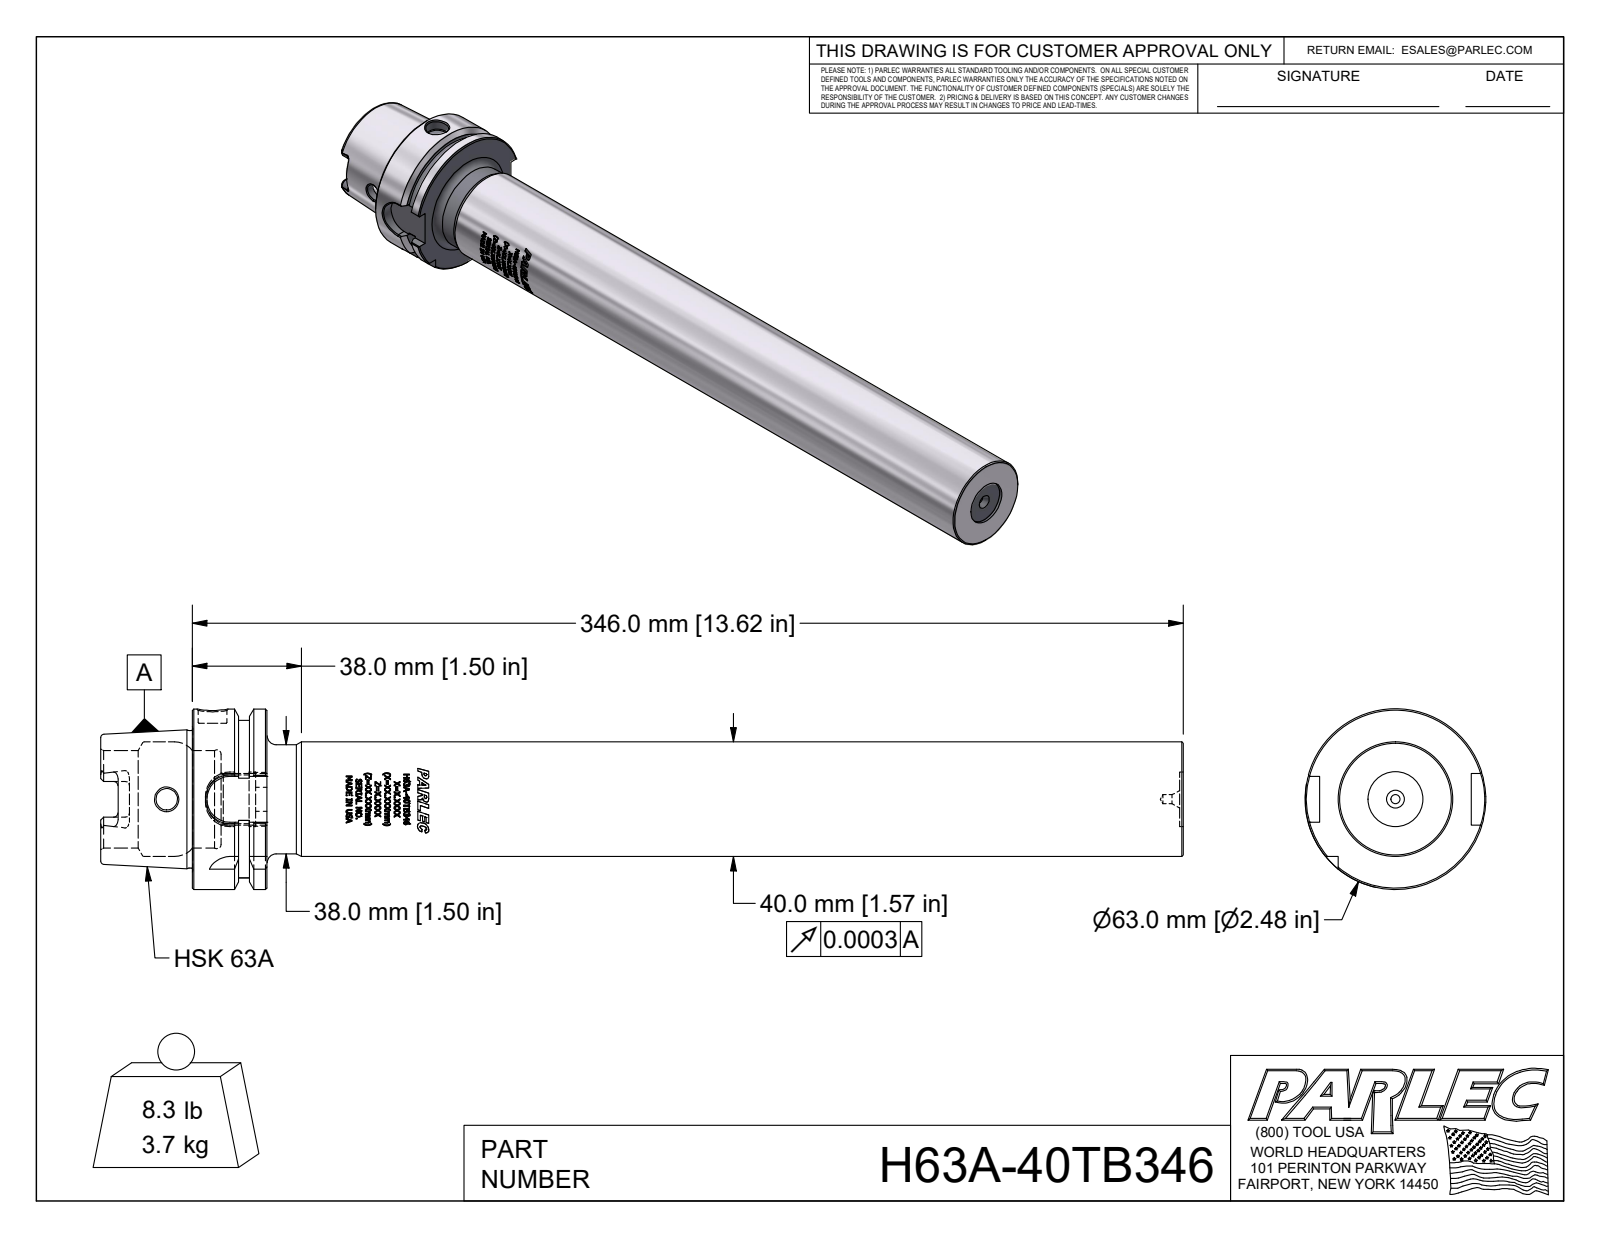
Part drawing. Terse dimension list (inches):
name: H63A-40TB346
written by: Autodesk Inventor 2022 (AUTOMOTIVE_DESIGN)
unit: in
bodies: 1 solid, 1193 faces (501 planar, 134 cylindrical, 558 other)
size: 14.882 × 2.48 × 2.48
volume: 29.4 in³; area: 97.37 in²
holes: 1× ⌀0.125, 1× ⌀0.295, 1× ⌀0.331, 1× ⌀0.394, 1× ⌀0.666, 1× ⌀0.749, 1× ⌀0.75, 1× ⌀1.339
bosses: 1× ⌀2.48, 1× ⌀1.891, 1× ⌀1.575, 1× ⌀1.496
rounds: 6× R0.059, 4× R0.113, 4× R0.315, 1× R0.787, 1× R1.083
face distances: 1.024, 13.622, 12.598, 0.241, 0.389, 0.394, 0.63, 13.228, 1.26, 1.654
